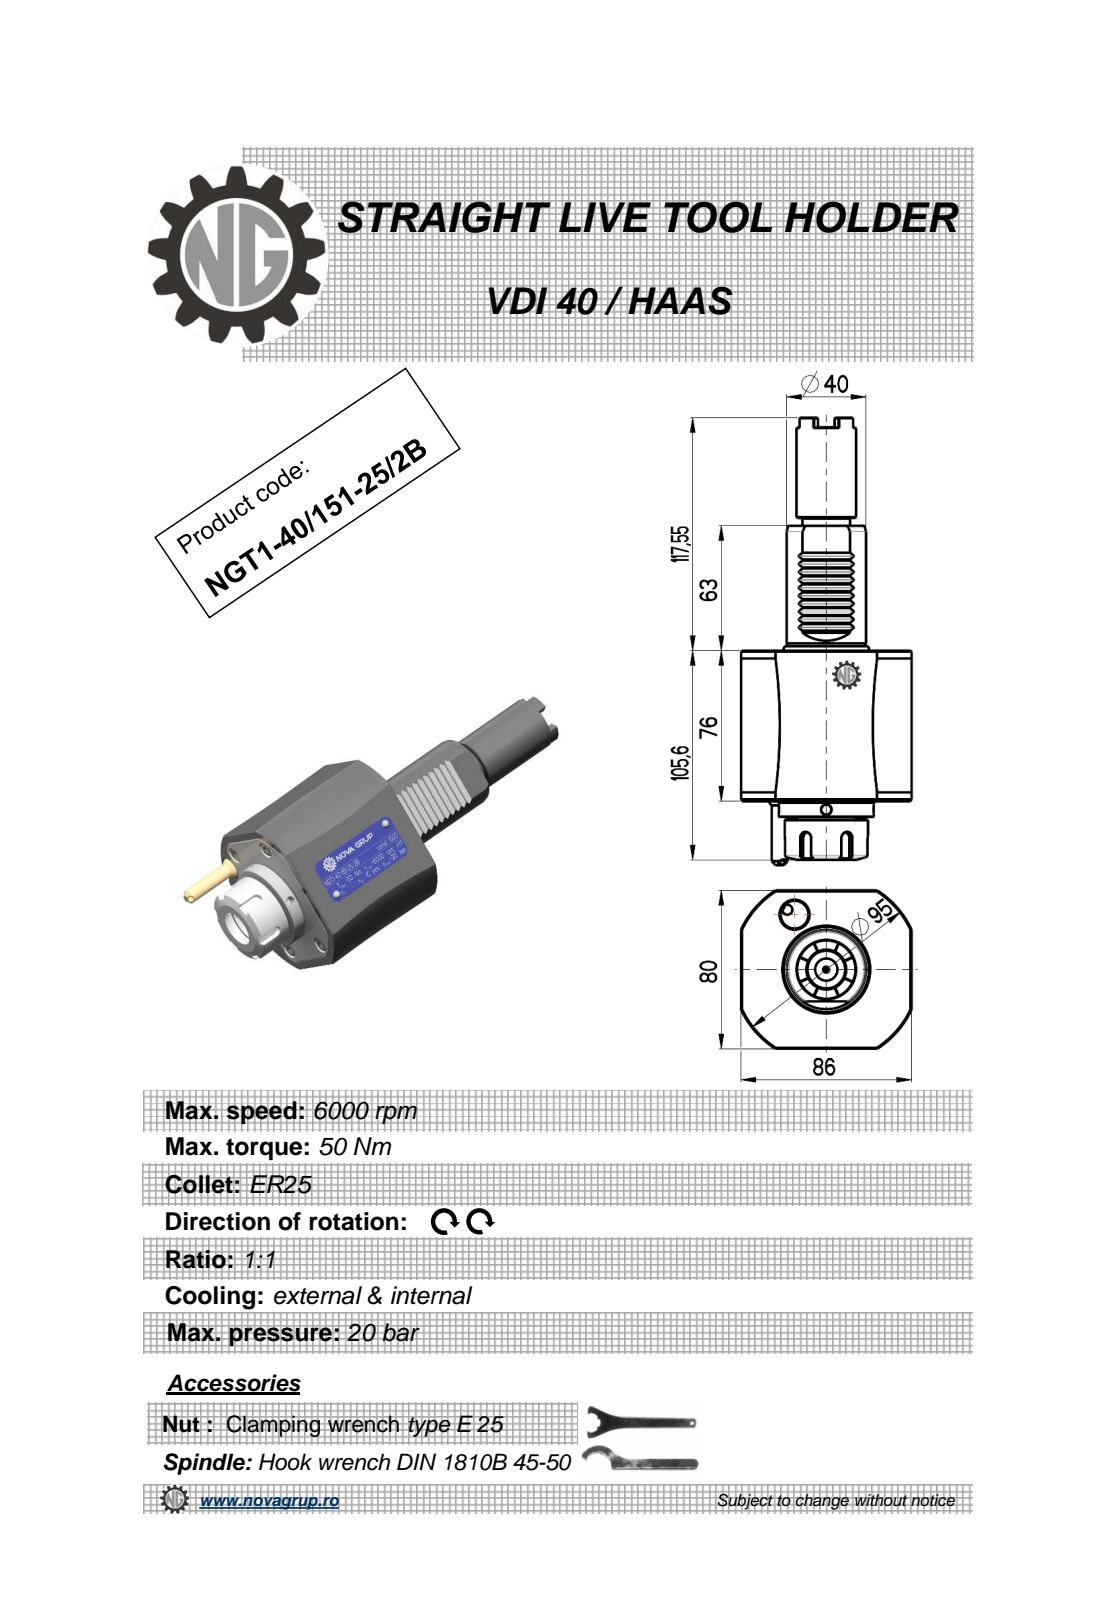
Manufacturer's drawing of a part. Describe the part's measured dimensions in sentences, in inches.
The part is named "NGT1_40_151_25_1B". Its 3-D file was written by "PRO/ENGINEER BY PARAMETRIC TECHNOLOGY CORPORATION, 2010280 (CONFIG_CONTROL_DESIGN)". It is 1 solid with 330 faces: 135 planar, 72 cylindrical and 123 other. Overall it measures 8.893 by 3.386 by 3.213 inches. Its volume is 38.14 cubic inches and its surface area 88.01 square inches. Round holes: 3 of diameter 0.197, 1 of diameter 0.118, 1 of diameter 0.768. Round bosses or shafts: 1 of diameter 1.89, 1 of diameter 1.654, 1 of diameter 1.634, 1 of diameter 1.575, 1 of diameter 1.299, 1 of diameter 1.181, 1 of diameter 0.945, 1 of diameter 0.315. Partial cylindrical surfaces (rounded edges, fillets, slot ends): 12 of radius 0.009, 10 of radius 0.012, 5 of radius 0.118, 1 of radius 1.87. The main face-to-face distances are 2.992, 3.15, 3.386, 3.307, 0.315, 0.111, 0.223, 2.48, 5.472, 5.787. The hole center spacings are 1.575.
